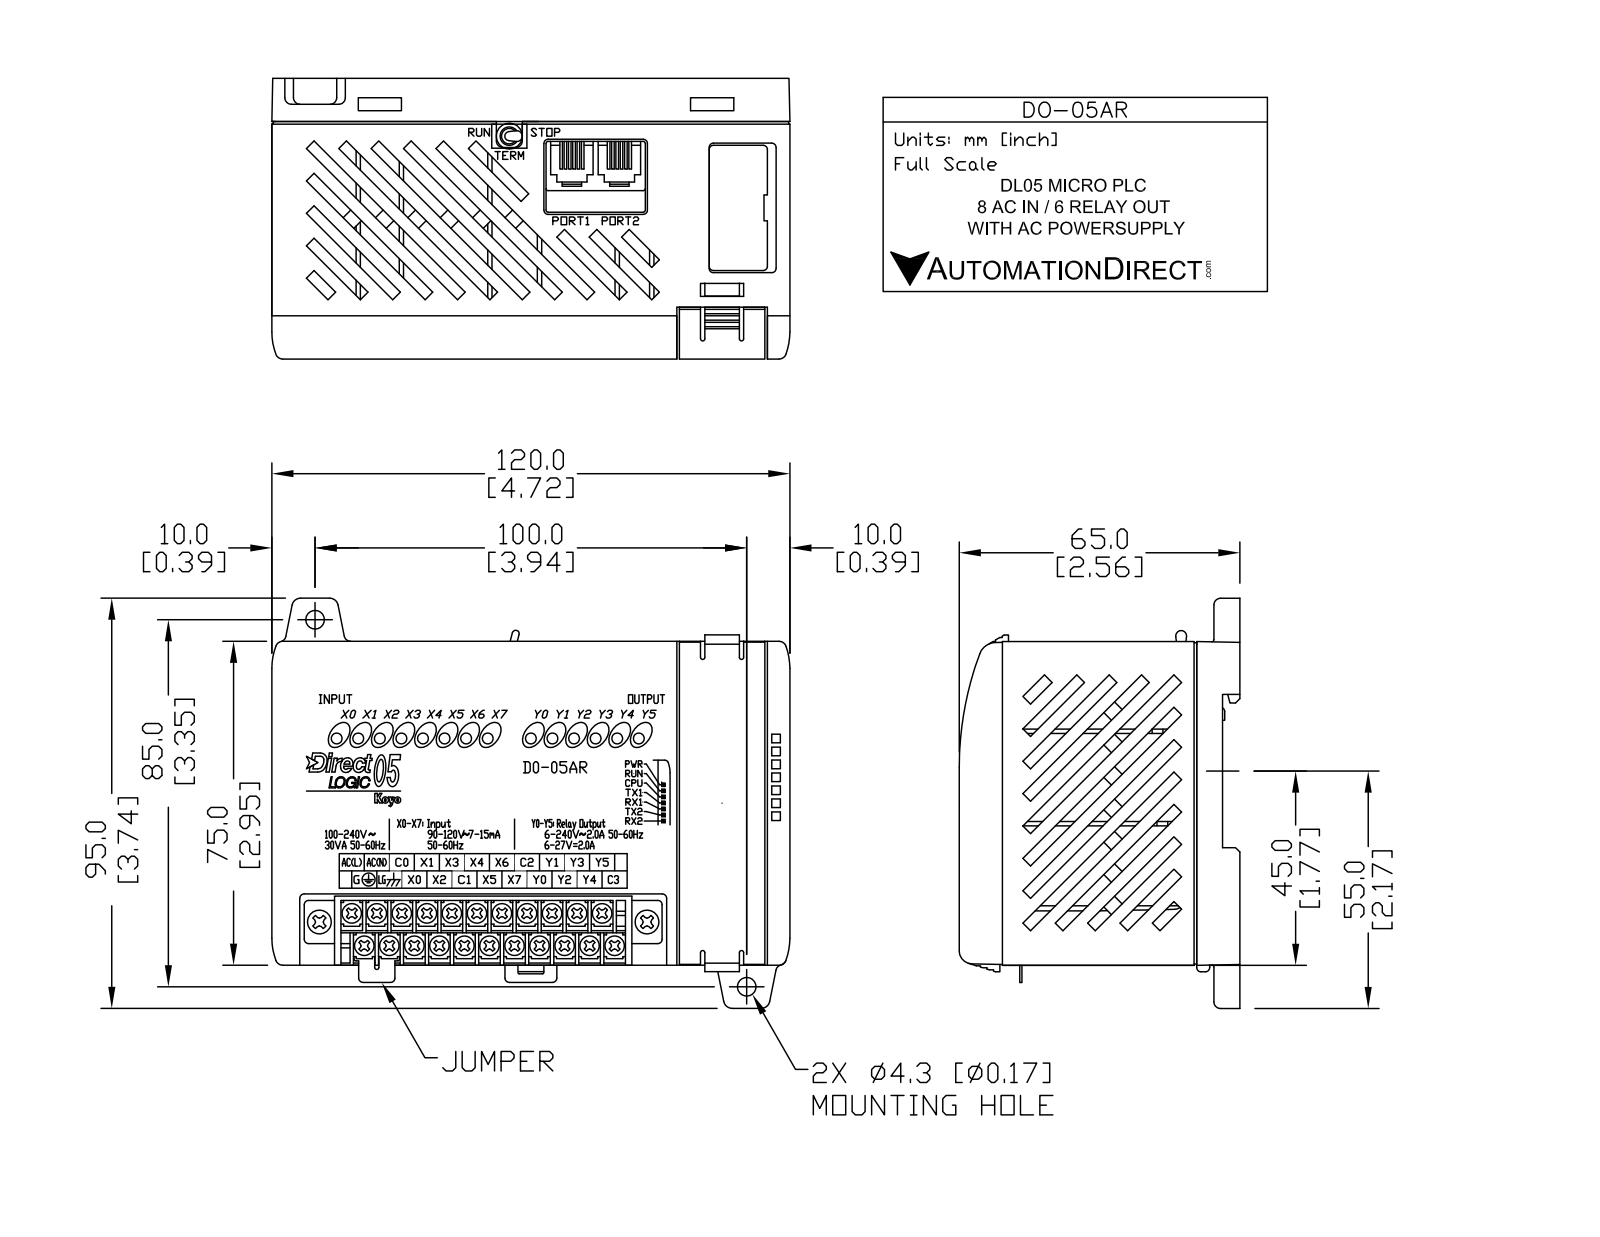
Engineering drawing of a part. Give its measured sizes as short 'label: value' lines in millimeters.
name: D0-05AR
written by: SolidWorks 2009 (AUTOMOTIVE_DESIGN)
unit: mm
bodies: 3 solids, 984 faces (681 planar, 95 cylindrical, 208 other)
size: 120 × 95 × 65.06
volume: 65 415 mm³; area: 91 009 mm²
holes: 2× ⌀4.3
bosses: 22× ⌀4.42, 2× ⌀4.5
rounds: 4× R1, 4× R2, 2× R1.5, 1× R63.5, 1× R65
face distances: 1.5, 73.5, 59.5, 4, 63.5, 118.5, 75, 72, 5.5, 65
hole spacings: 131.24
